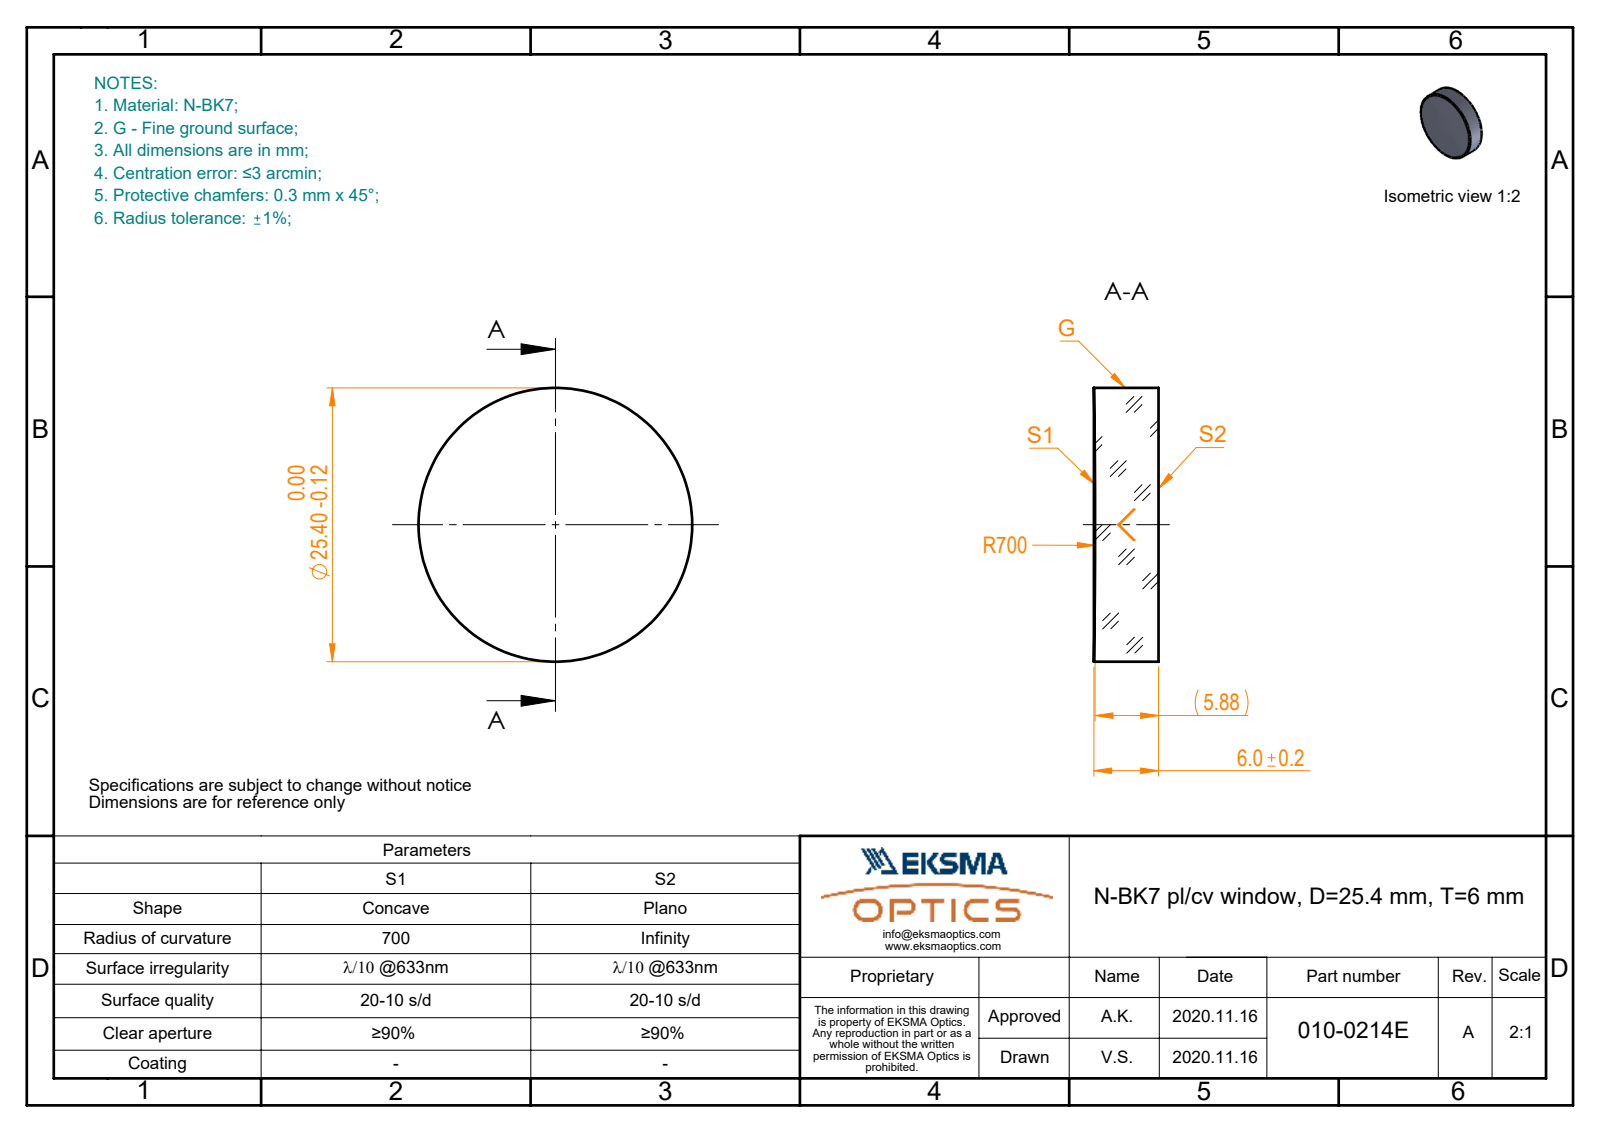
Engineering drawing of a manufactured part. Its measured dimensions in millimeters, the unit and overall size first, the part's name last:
Units: millimetres
Overall size (bounding box): 25.4 × 25.4 × 6
Round bosses / shafts (diameter × count): ⌀25.4 ×1
Volume: 3 011 mm³ · Surface area: 1 492 mm²
Bodies: 1 solid, 5 faces (1 planar, 2 cylindrical, 2 other)
Part name (STEP PRODUCT): 010-0214E_N-BK7_PCV_window
STEP written by: SolidWorks 2019 (CONFIG_CONTROL_DESIGN)
